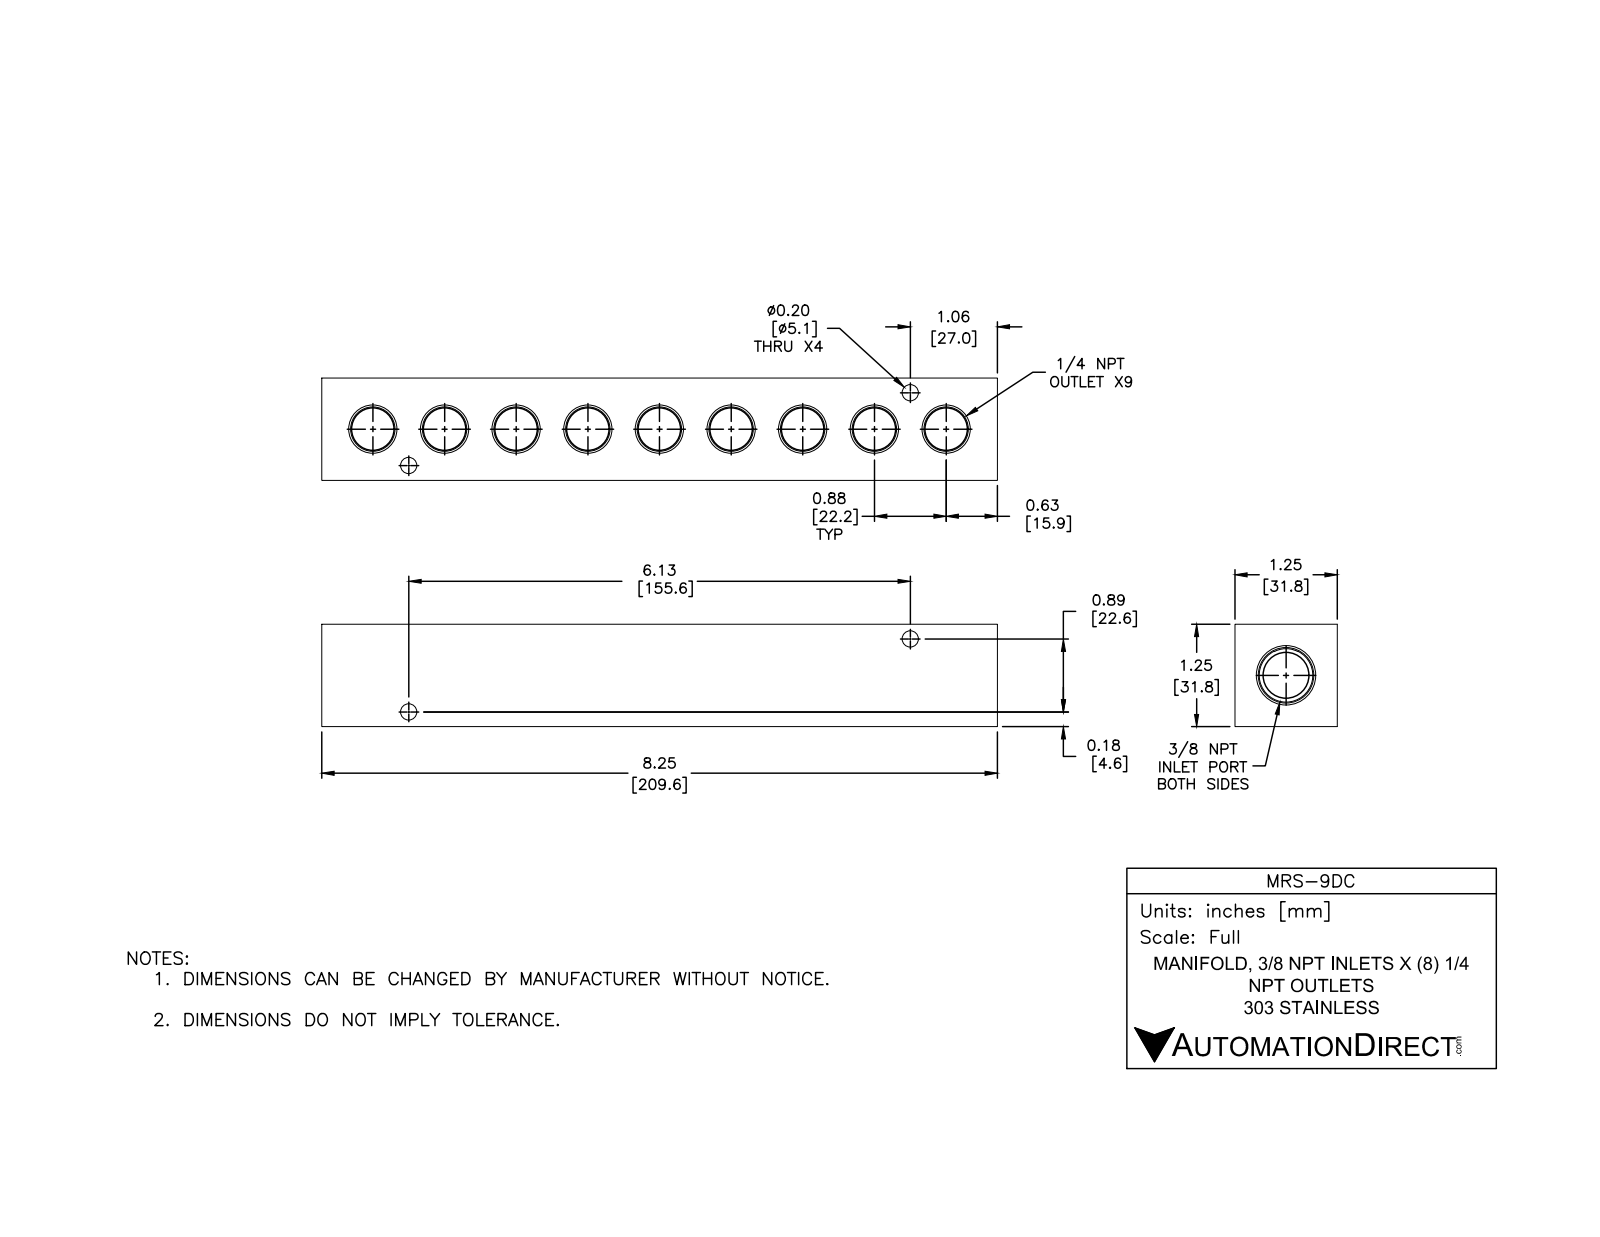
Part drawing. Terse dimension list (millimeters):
name: MRS-9DC
written by: SolidWorks 2015 (CONFIG_CONTROL_DESIGN)
unit: mm
bodies: 1 solid, 106 faces (26 planar, 36 cylindrical, 44 other)
size: 209.6 × 31.8 × 31.8
volume: 161 800 mm³; area: 40 820 mm²
holes: 4× ⌀5.1, 1× ⌀14.3
rounds: 9× R5.6
face distances: 31.8, 209.6, 21.8, 9.9, 10.4, 199.1, 188.7
hole spacings: 157.2
